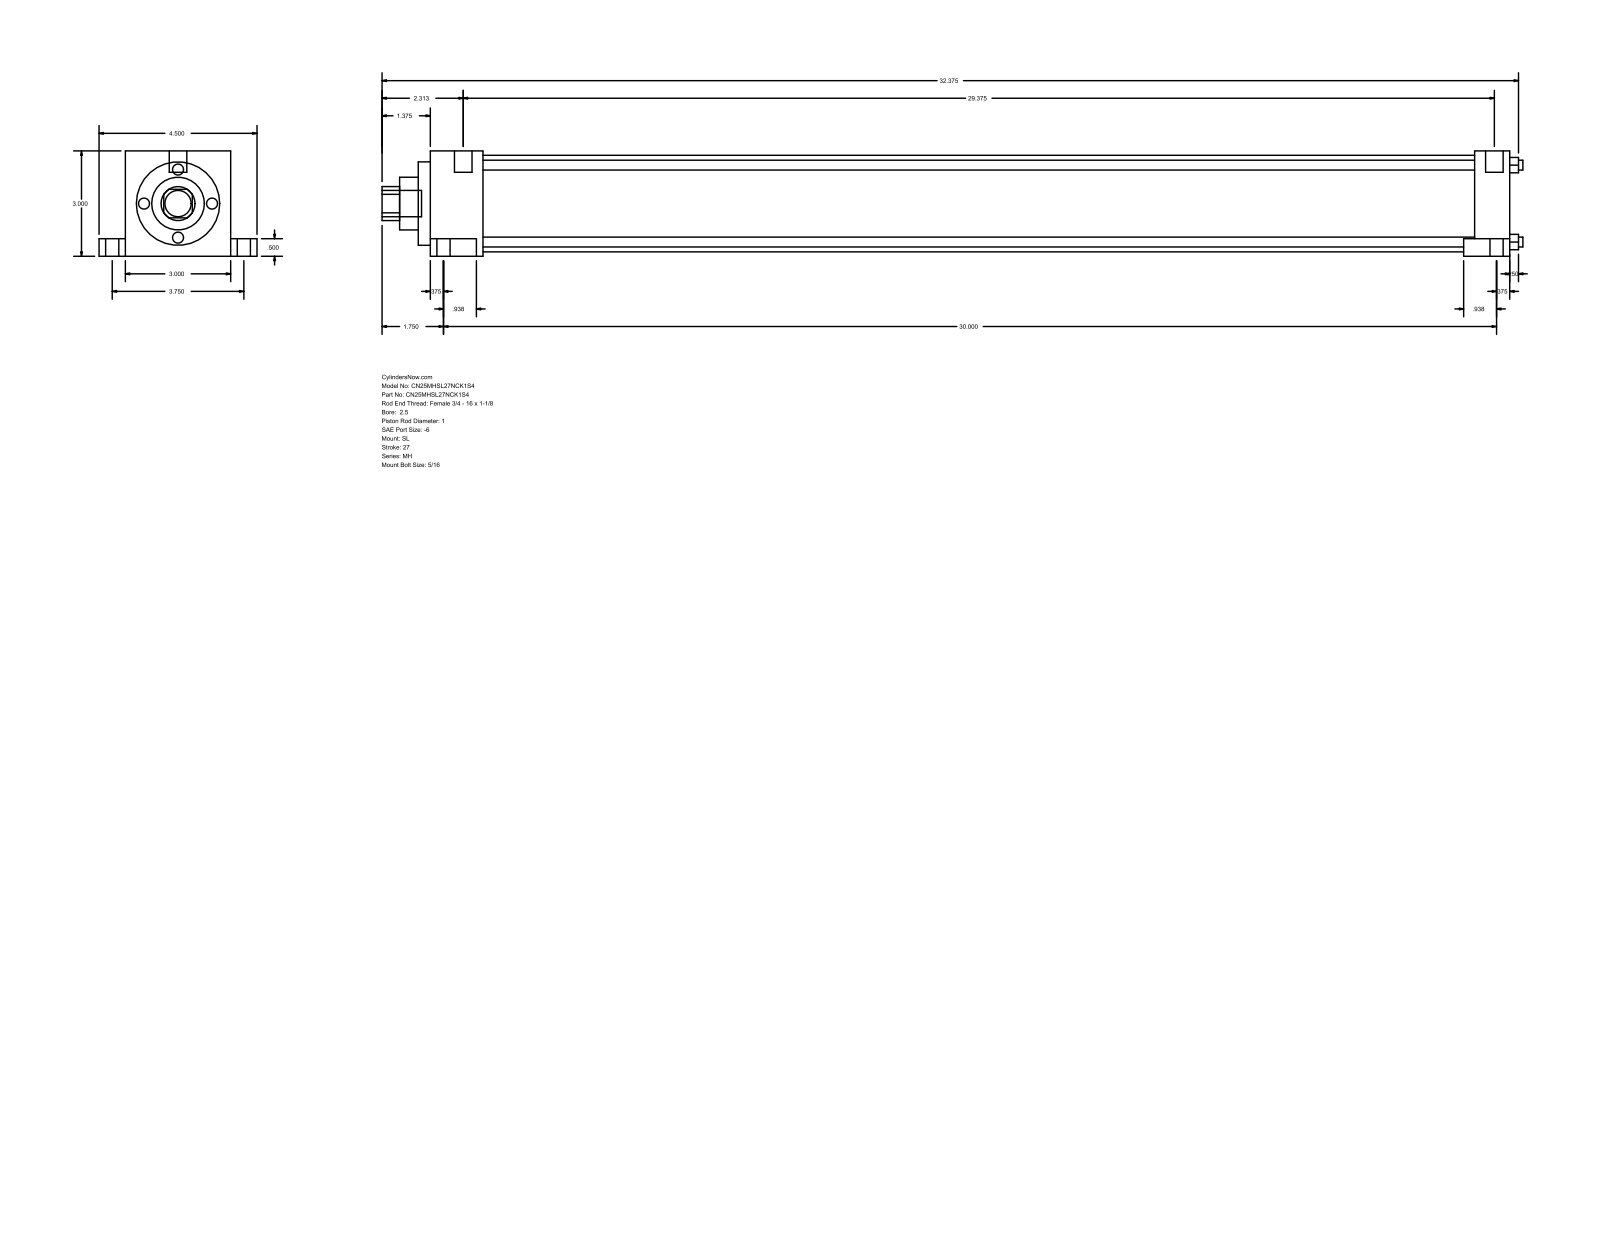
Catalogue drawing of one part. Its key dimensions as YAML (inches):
part_name: "MH_SL__0250_1"
step_written_by: "GSSL Pune (CONFIG_CONTROL_DESIGN)"
units: inches
bodies: {solids: 0, faces: 86, planar: 61, cylindrical: 25, other: 0}
overall_size: [32.5, 4.5, 3]
round_holes:
  - {diameter: 0.281, count: 4}
  - {diameter: 1, count: 1}
  - {diameter: 1.5, count: 1}
  - {diameter: 2.375, count: 1}
  - {diameter: 2.75, count: 1}
round_bosses_or_shafts:
  - {diameter: 0.625, count: 2}
  - {diameter: 0.375, count: 2}
  - {diameter: 0.219, count: 2}
  - {diameter: 0.75, count: 1}
  - {diameter: 0.5, count: 1}
partial_cylinders:
  - {radius: 0.484, count: 1}
face_to_face_distances: [3, 1, 30.094, 31.094, 0.5, 2.5, 0.75, 3.75, 0.531, 30.625]
hole_center_spacings: [1.548, 2.19, 3.097]
